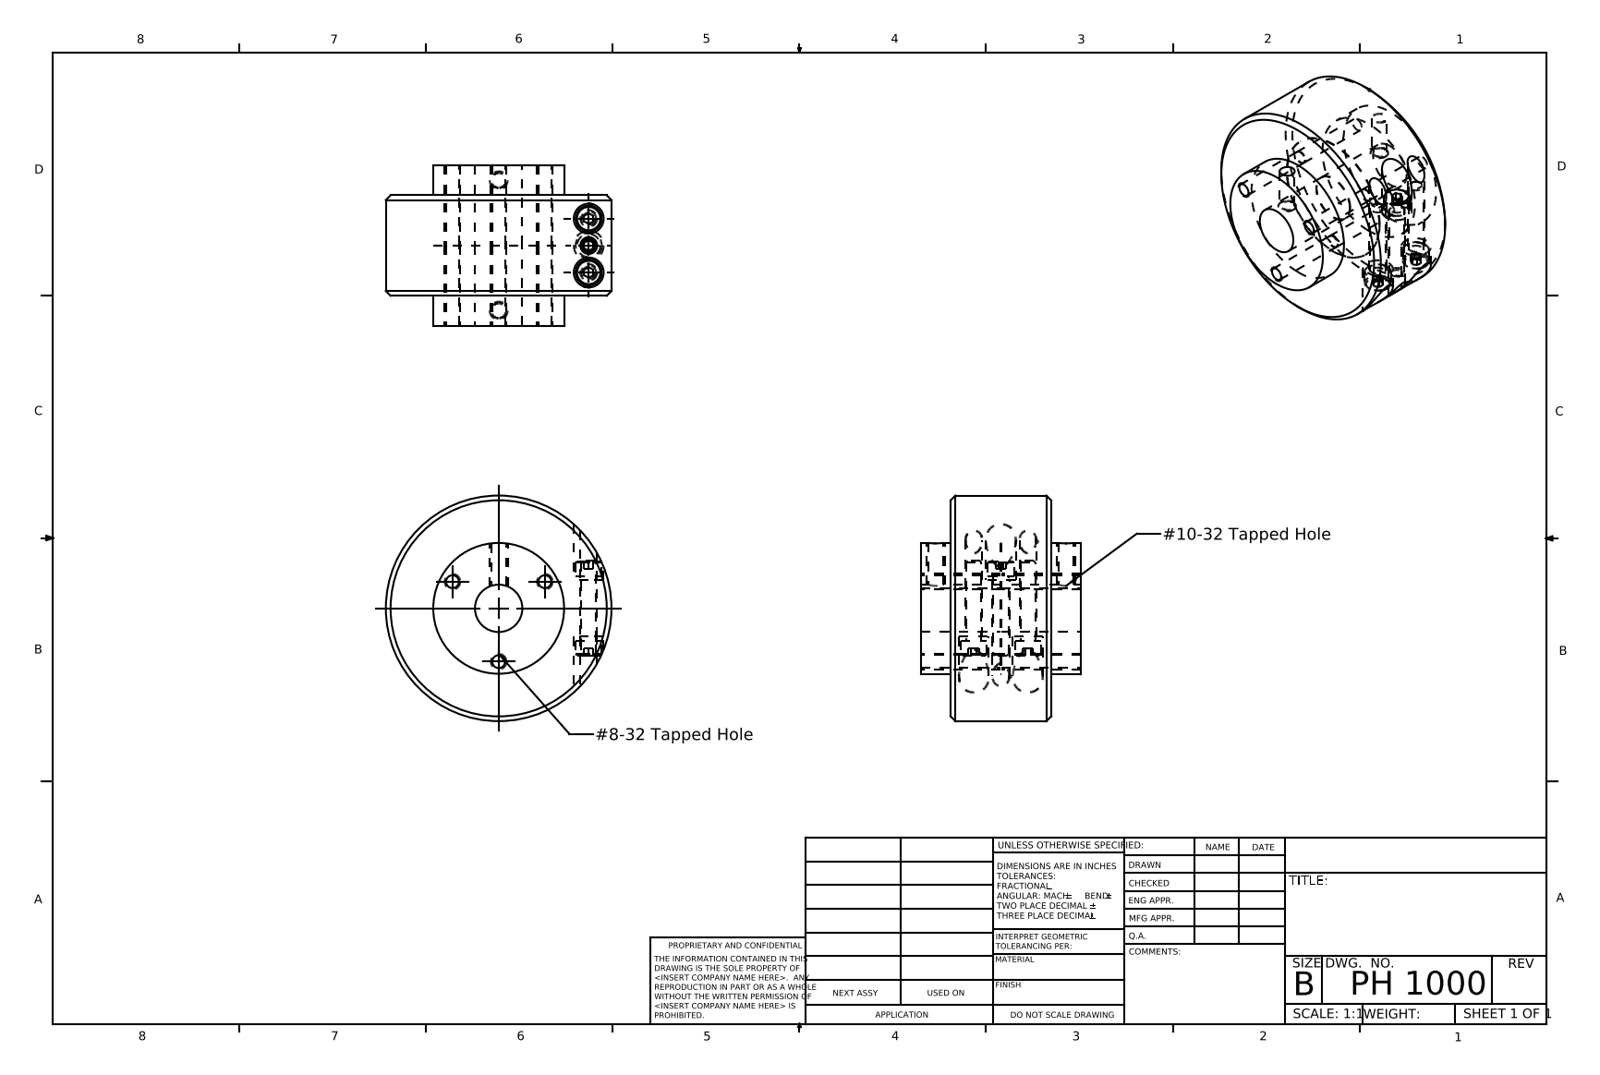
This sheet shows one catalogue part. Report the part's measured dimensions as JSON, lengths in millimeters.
{"part_name": "PH 1000", "step_written_by": "SolidWorks 2010 (CONFIG_CONTROL_DESIGN)", "units": "millimeters", "bodies": {"solids": 4, "faces": 107, "planar": 39, "cylindrical": 52, "other": 16}, "overall_size": [60.5, 60.5, 42.9], "volume_mm3": 83840, "surface_area_mm2": 19910, "round_holes": [[3.5, 3], [4.5, 3], [8, 3], [4, 2], [12.7, 1]], "round_bosses_or_shafts": [[7, 3], [4, 3], [60.5, 1], [35.1, 1]], "face_to_face_distances": [26.9, 8, 34.9, 21.4, 21.5, 13.4, 13.5, 42.9, 1, 4], "hole_center_spacings": [24.7, 7.2, 14.3, 26.2, 29.8, 34.5, 14.3, 14.5]}
